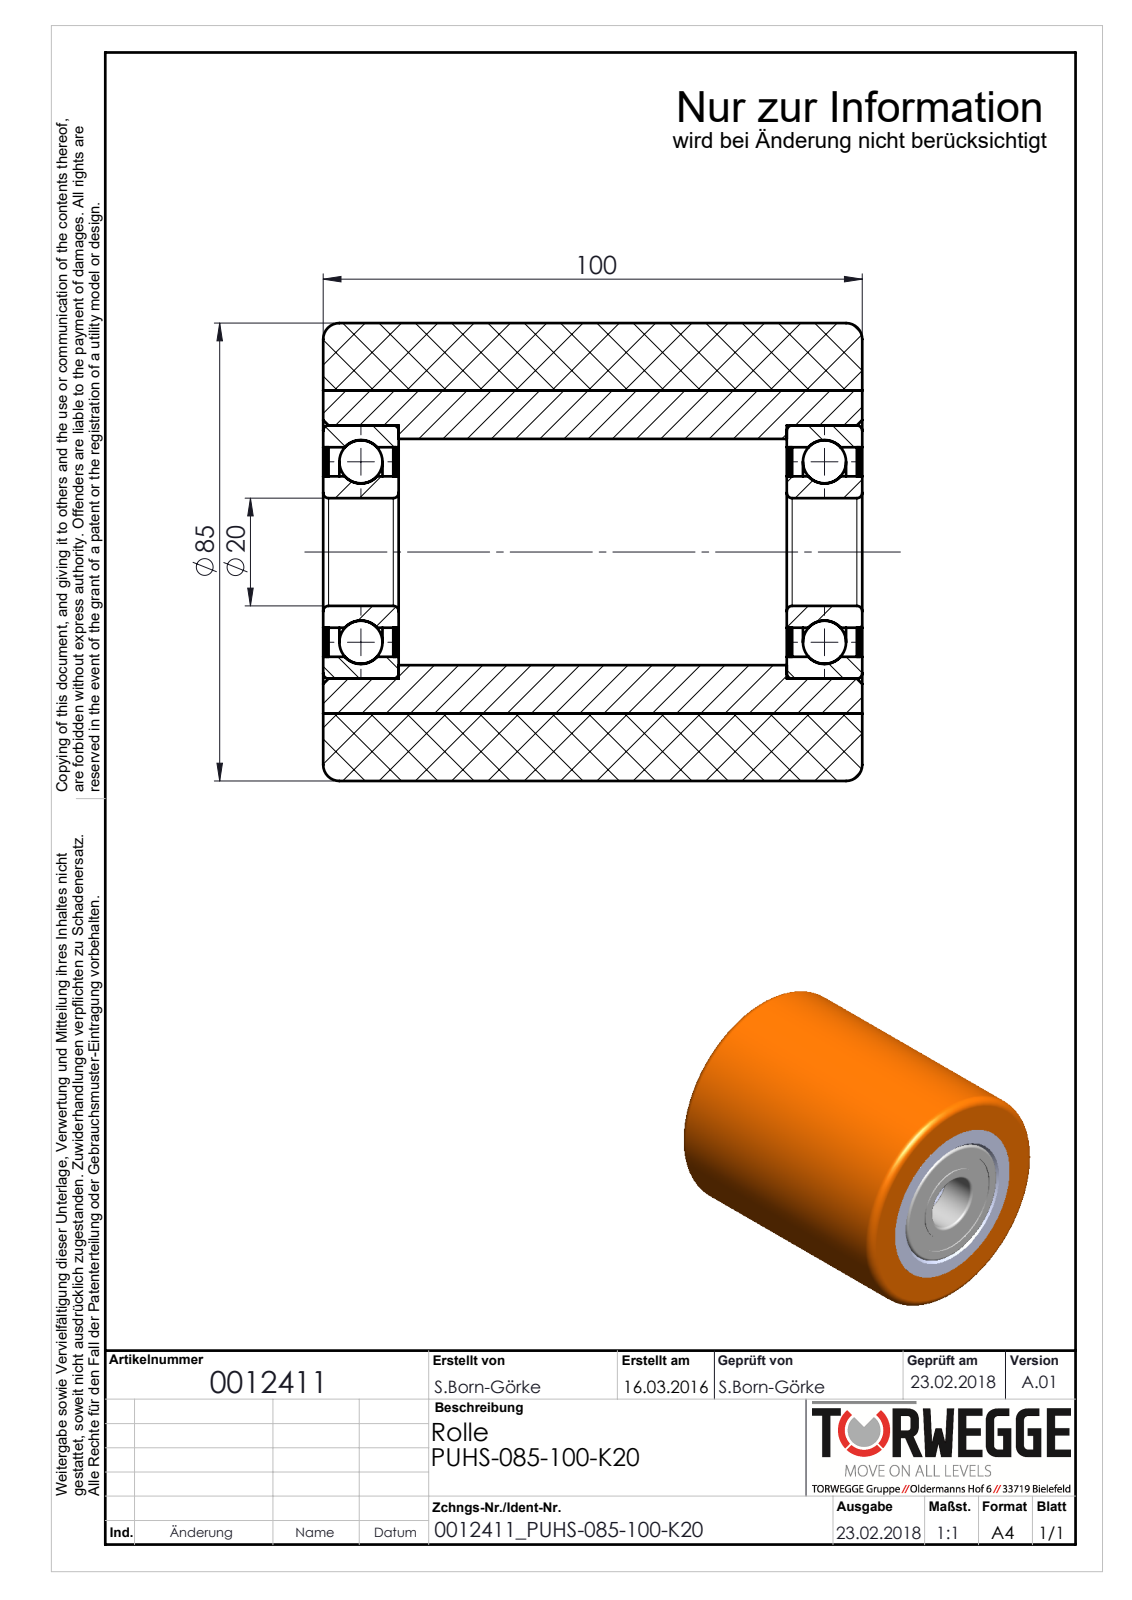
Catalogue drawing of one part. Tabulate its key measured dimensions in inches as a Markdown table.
| quantity | value |
| --- | --- |
| part name | 0012411_PUHS-085-100-K20 |
| STEP written by | SolidWorks 2016 (AUTOMOTIVE_DESIGN) |
| units | inches |
| bodies | 12 solids, 118 faces (22 planar, 52 cylindrical, 44 other) |
| overall size | 3.937 × 3.346 × 3.346 |
| volume | 27.51 in³ |
| surface area | 172.3 in² |
| round holes (diameter × count) | 0.787 × 1, 1.106 × 1, 1.531 × 1, 1.654 × 1, 1.85 × 1, 2.362 × 1 |
| round bosses / shafts (diameter × count) | 3.346 × 1 |
| main face-to-face distances | 0.02, 3.386, 3.937, 0.512, 0.039, 0.531, 3.406, 0.492, 3.366, 0.551 |
